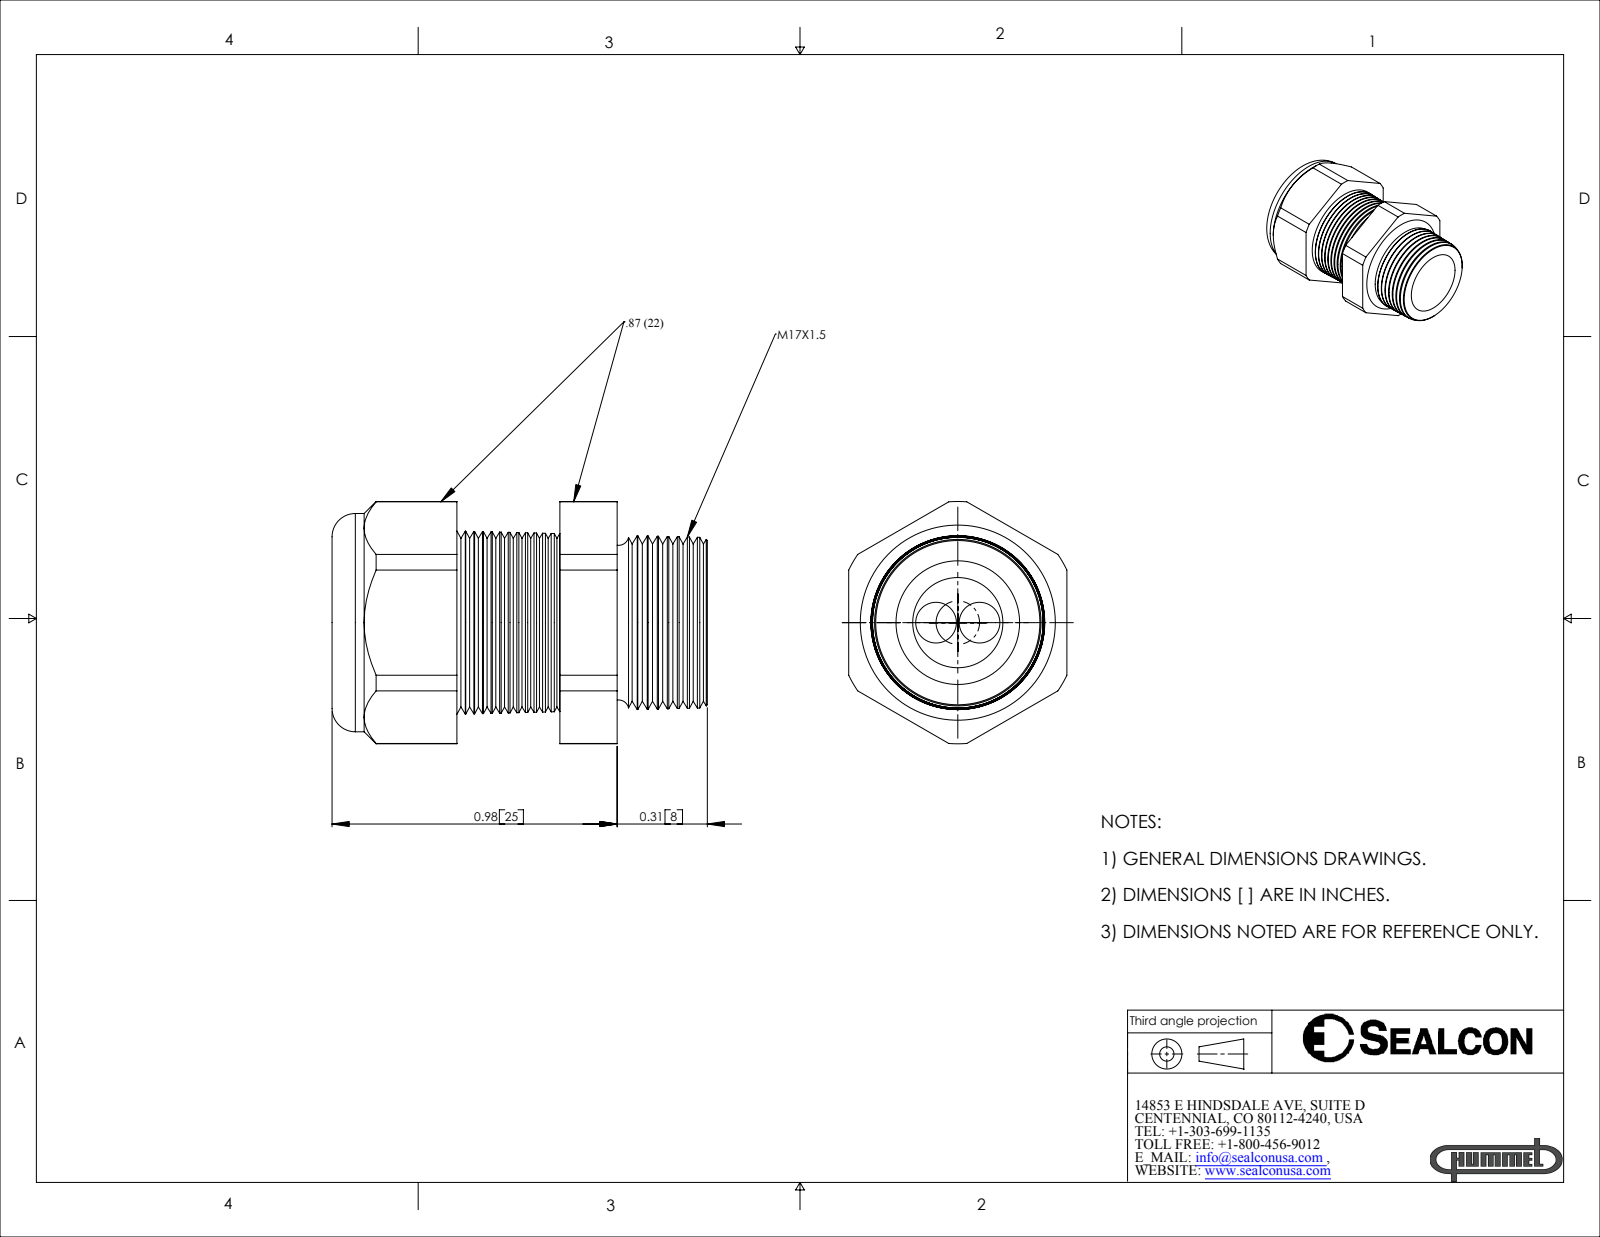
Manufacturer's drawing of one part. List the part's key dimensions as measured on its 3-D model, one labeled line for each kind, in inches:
Part name (STEP PRODUCT): CD17M3-BK
STEP written by: SolidWorks 2007 (CONFIG_CONTROL_DESIGN)
Units: inches
Bodies: 2 solids, 183 faces (21 planar, 24 cylindrical, 138 other)
Overall size (bounding box): 1.29 × 0.833 × 0.75
Volume: 0.353 in³ · Surface area: 6.652 in²
Round holes (diameter × count): ⌀0.14 ×2, ⌀0.29 ×1, ⌀0.31 ×1
Round bosses / shafts (diameter × count): ⌀0.75 ×1
Partial cylindrical surfaces — rounded edges, fillets, slot ends (radius × count): R0.416 ×1
Main face-to-face distances: 0.75, 0.75, 0.783, 0.429, 0.354, 0.98, 0.551, 0.197, 1.29, 0.861
Hole centre spacings: 0.075, 0.15
